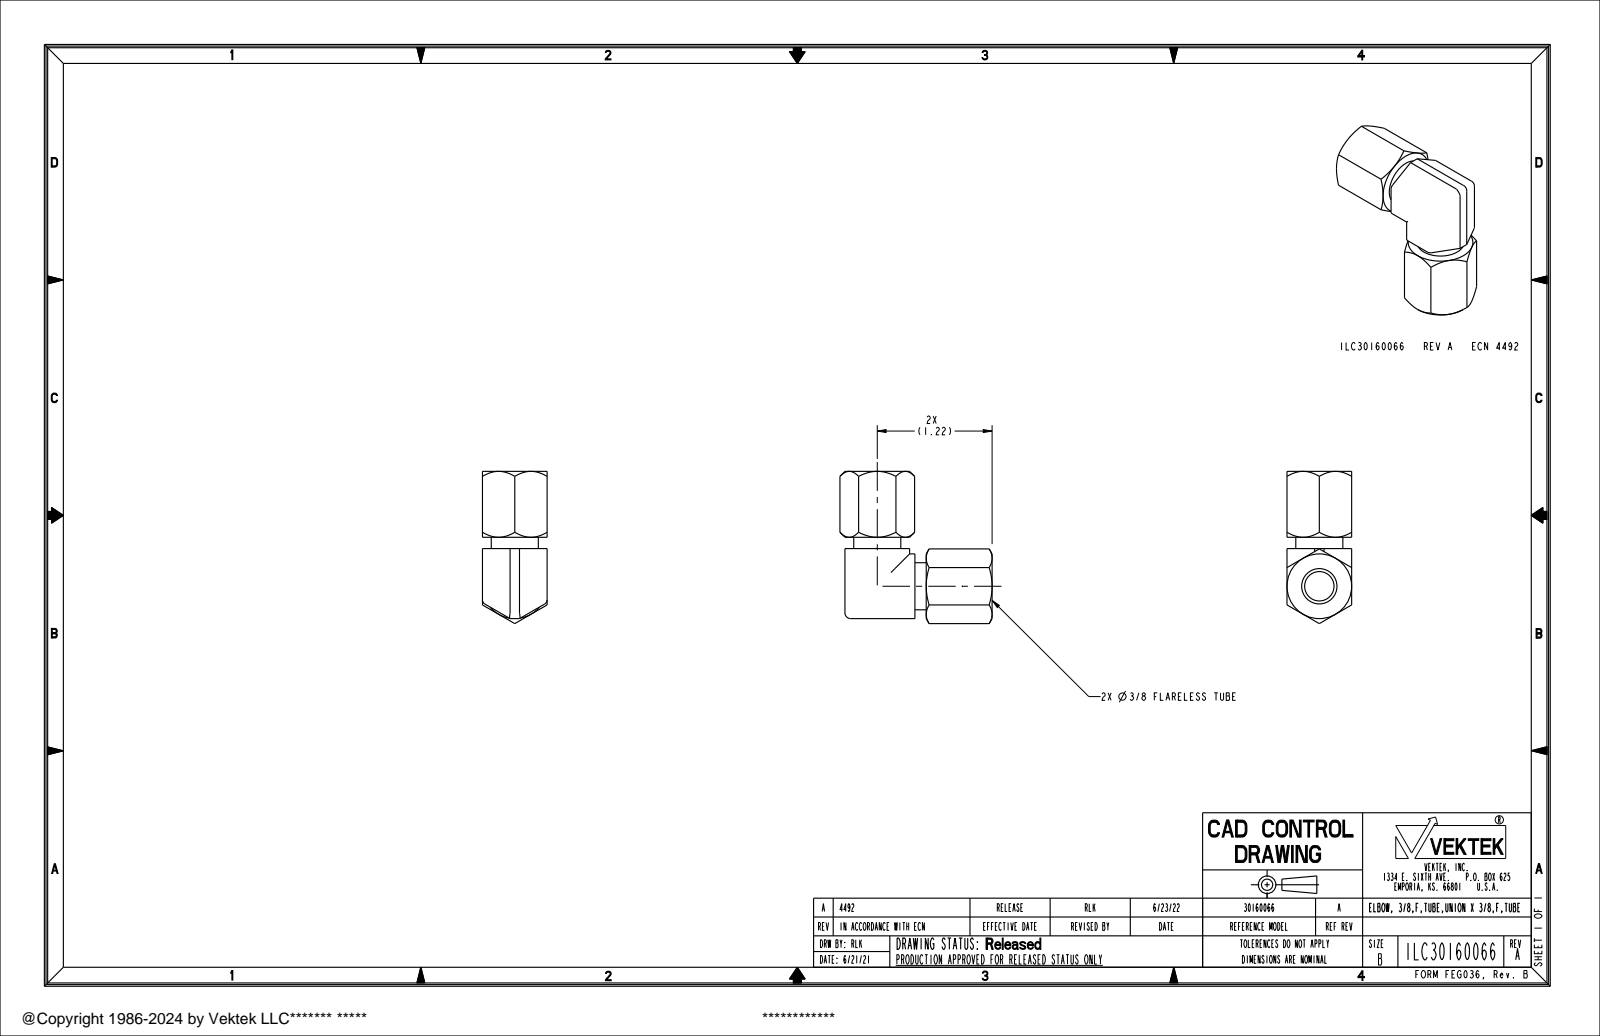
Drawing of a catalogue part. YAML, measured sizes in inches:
part_name: "ILC30160066"
step_written_by: "CREO PARAMETRIC BY PTC INC, 2021164 (AUTOMOTIVE_DESIGN)"
units: inches
bodies: {solids: 1, faces: 89, planar: 36, cylindrical: 27, other: 26}
overall_size: [1.617, 1.617, 0.687]
volume: 0.678
surface_area: 9.573
round_holes:
  - {diameter: 0.312, count: 2}
  - {diameter: 0.375, count: 2}
round_bosses_or_shafts:
  - {diameter: 0.5, count: 2}
partial_cylinders:
  - {radius: 0.05, count: 8}
  - {radius: 0.06, count: 3}
face_to_face_distances: [0.687, 0.021, 0.666, 0.687, 0.666, 0.82, 0.7, 0.12, 0.645, 1.563]
